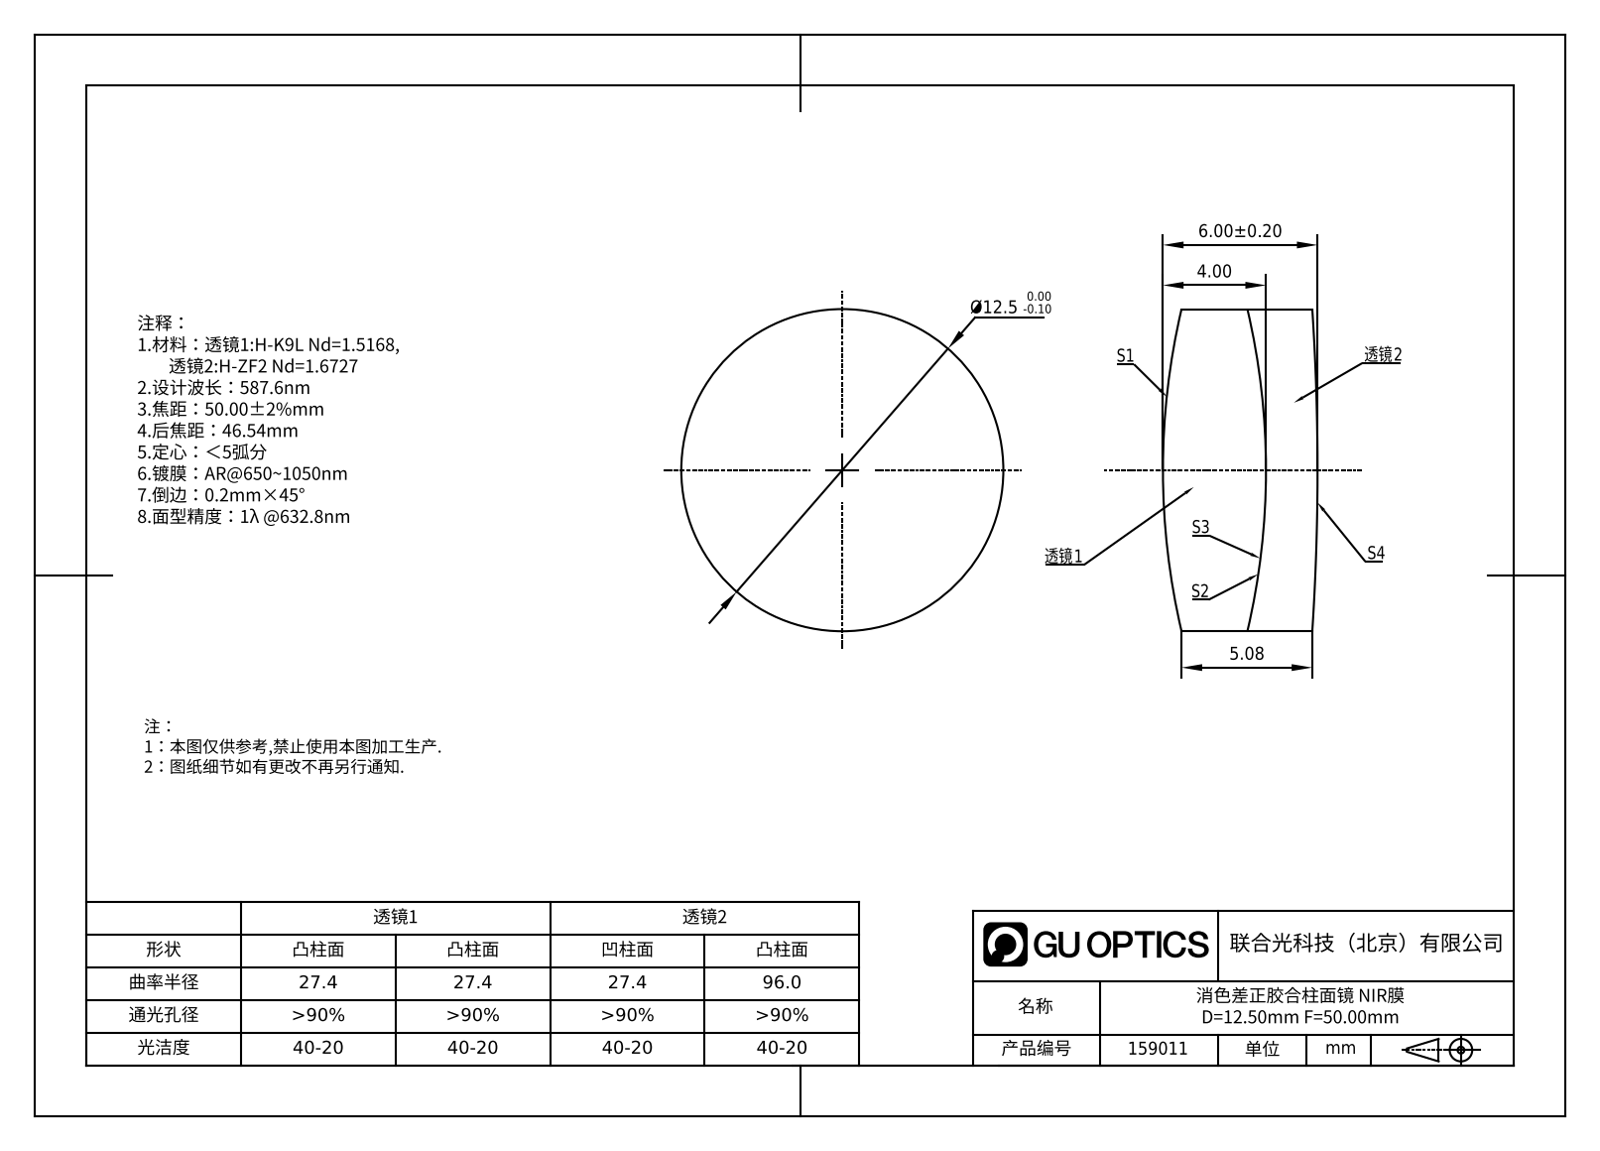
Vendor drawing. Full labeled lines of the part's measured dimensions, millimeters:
Part name (STEP PRODUCT): 159011
STEP written by: SolidWorks 2020 (CONFIG_CONTROL_DESIGN)
Units: millimetres
Bodies: 1 solid, 5 faces (0 planar, 5 cylindrical, 0 other)
Overall size (bounding box): 12.5 × 12.5 × 6
Volume: 708 mm³ · Surface area: 464 mm²
Round bosses / shafts (diameter × count): ⌀12.5 ×1
Partial cylindrical surfaces — rounded edges, fillets, slot ends (radius × count): R27.4 ×1, R96 ×1
